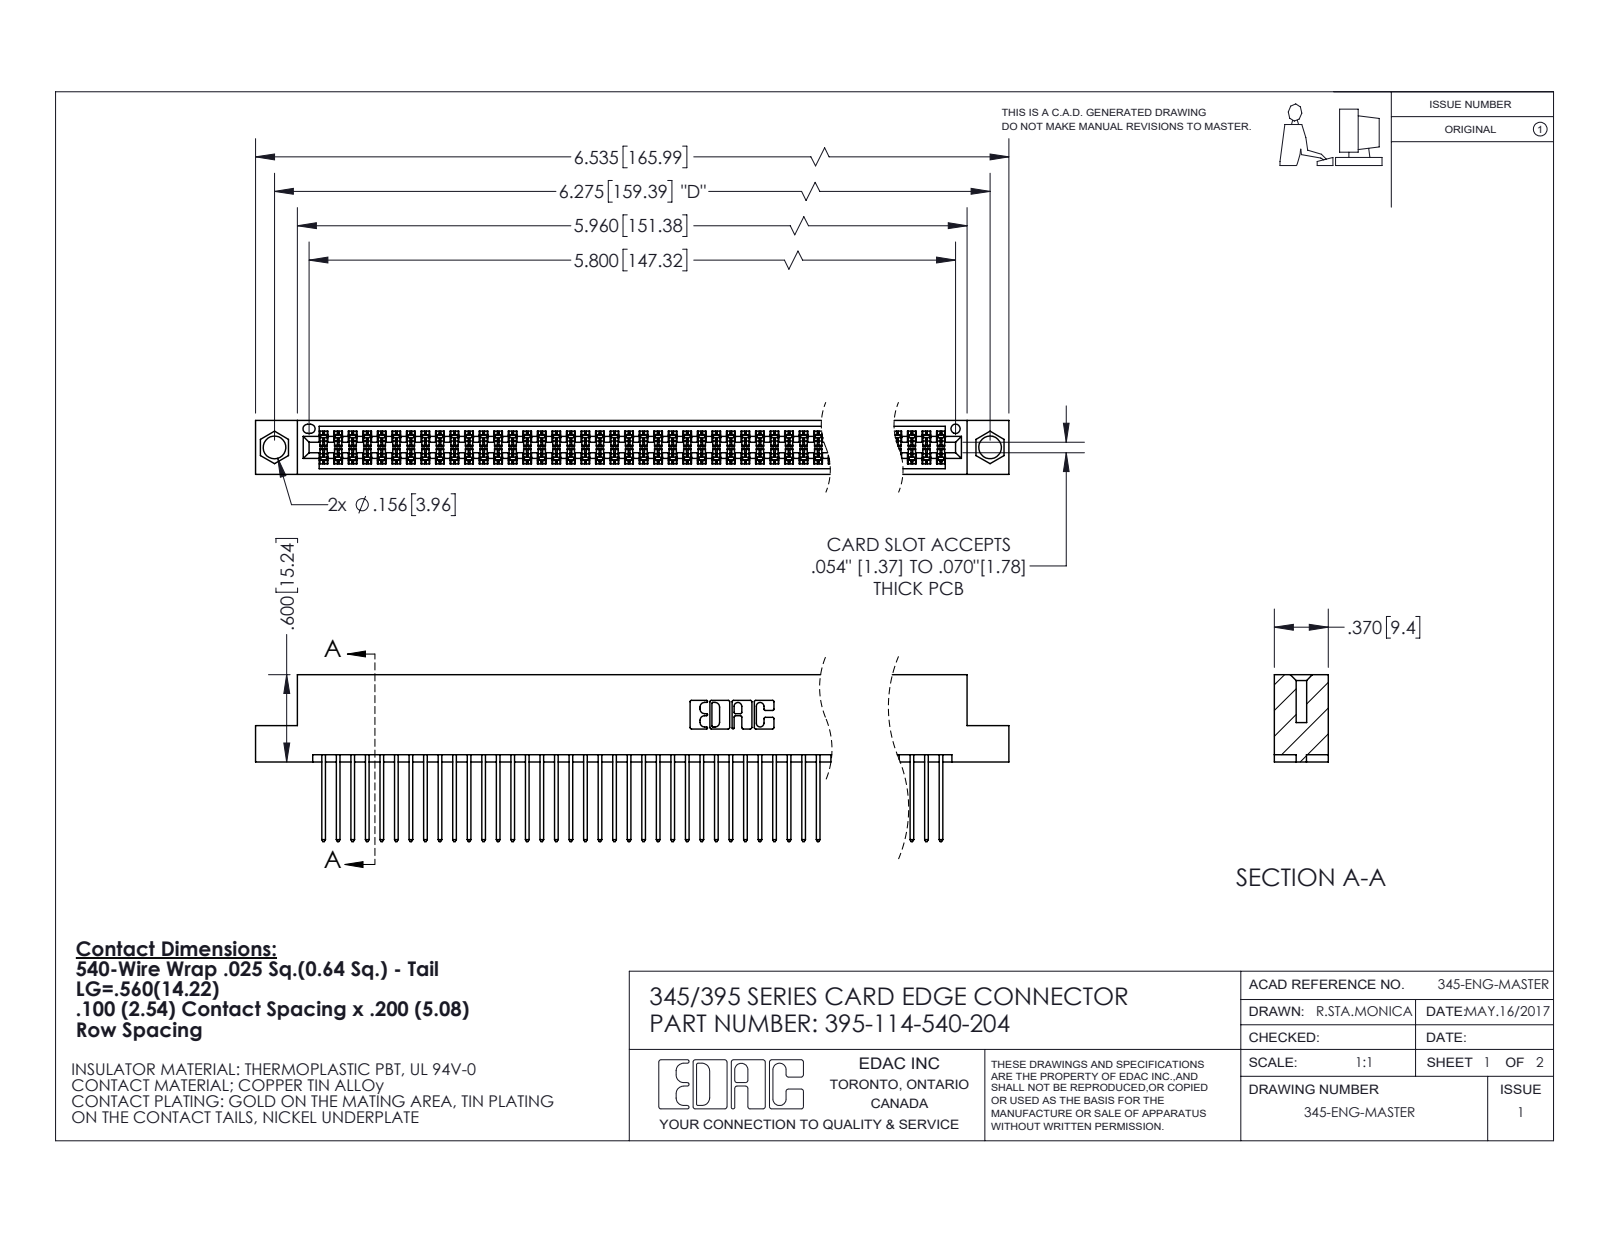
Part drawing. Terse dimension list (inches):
name: 395-114-540-204; 345 Part_Flush Mounting Lugs - 0.156 Dia-TI; 345-292-001_345-293-140
written by: SolidWorks 2020 (CONFIG_CONTROL_DESIGN)
unit: in
bodies: 115 solids, 5840 faces (3856 planar, 1984 cylindrical, 0 other)
size: 6.535 × 1.147 × 0.37
volume: 1.012 in³; area: 41.34 in²
holes: 2× ⌀0.156, 1× ⌀0.064
rounds: 228× R0.006, 114× R0.01, 22× R0.01, 6× R0.007, 6× R0.031, 3× R0.026, 2× R0.014, 2× R0.019
face distances: 0.298, 0.072, 0.2, 0.098, 0.272, 0.025, 0.37, 0.225, 0.175, 0.149
hole spacings: 0.27, 6.039, 6.275
